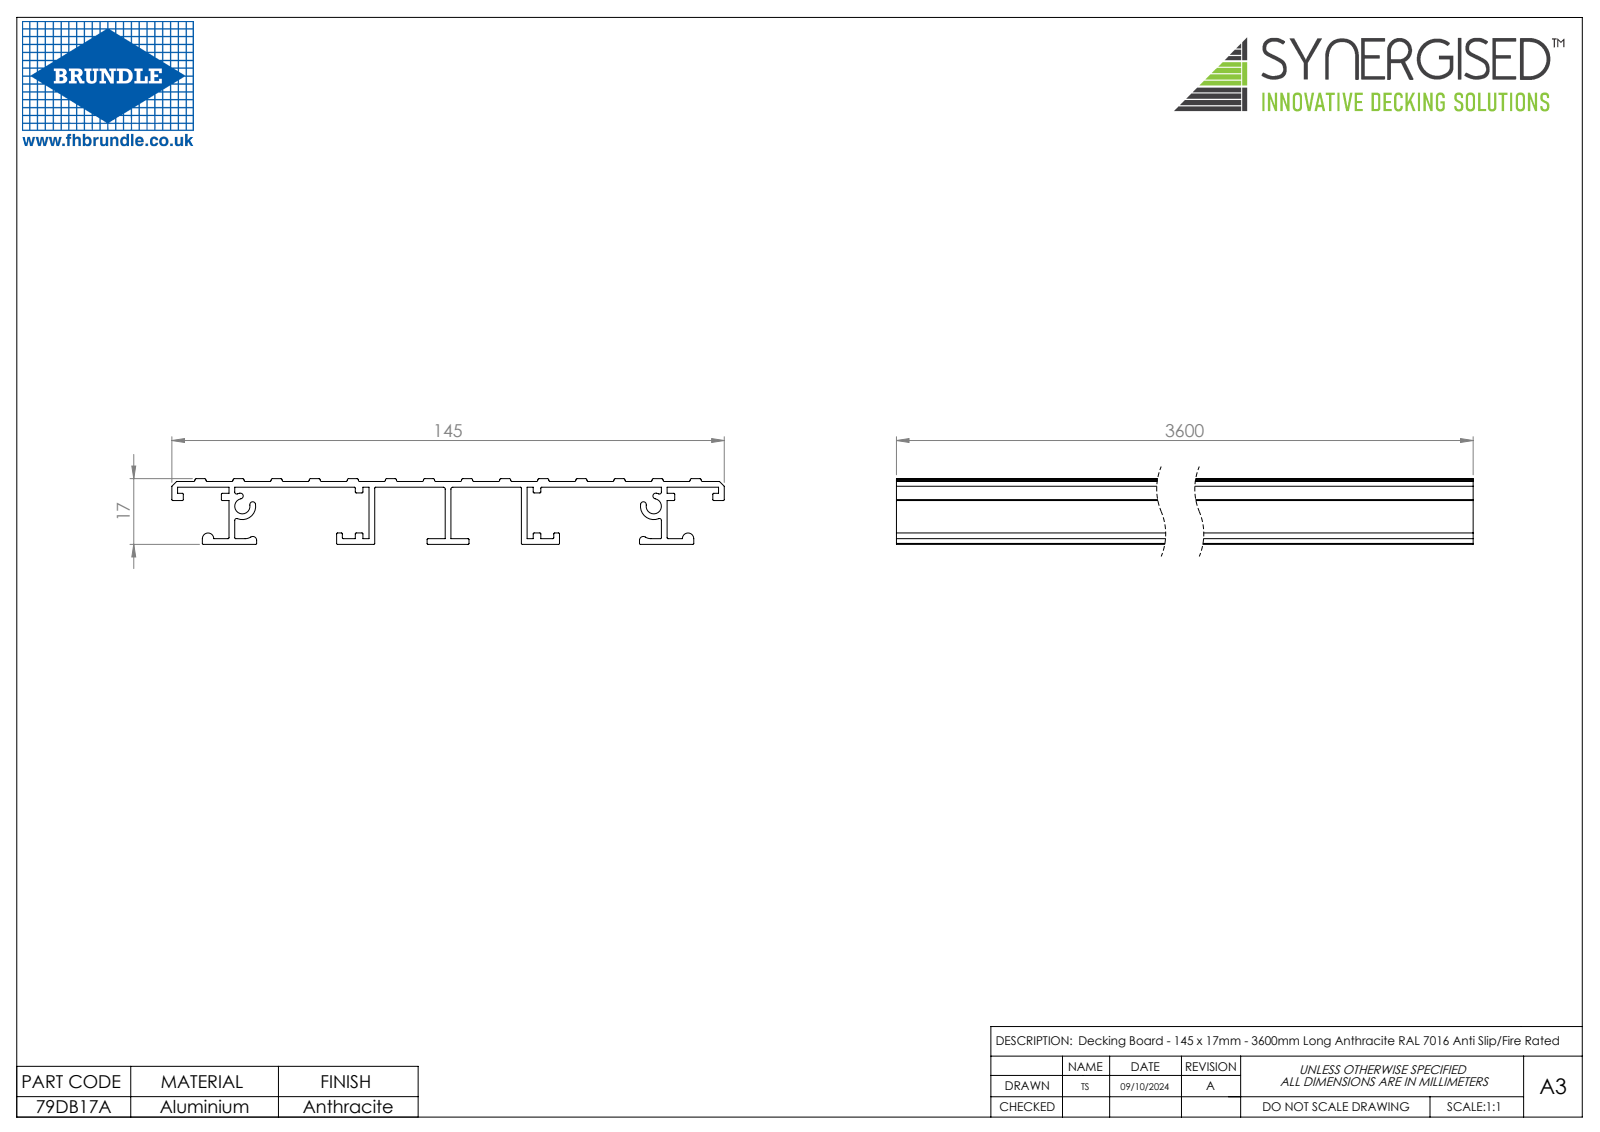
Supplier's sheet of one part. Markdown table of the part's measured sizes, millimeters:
| quantity | value |
| --- | --- |
| part name | 79DB17A |
| STEP written by | SolidWorks 2023 (CONFIG_CONTROL_DESIGN) |
| units | millimeters |
| bodies | 1 solid, 267 faces (110 planar, 157 cylindrical, 0 other) |
| overall size | 3600 × 145 × 17.25 |
| volume | 1 859 000 mm³ |
| surface area | 2 291 000 mm² |
| partial cylindrical surfaces (radius × count) | 0.3 × 56, 0.25 × 44, 1.5 × 16, 0.5 × 6, 0.75 × 4, 1 × 2, 2 × 2, 2.75 × 2 |
| main face-to-face distances | 1.5, 15, 16.5, 20, 13.5, 36.75, 56.75, 76.75, 17.25, 2.25 |
